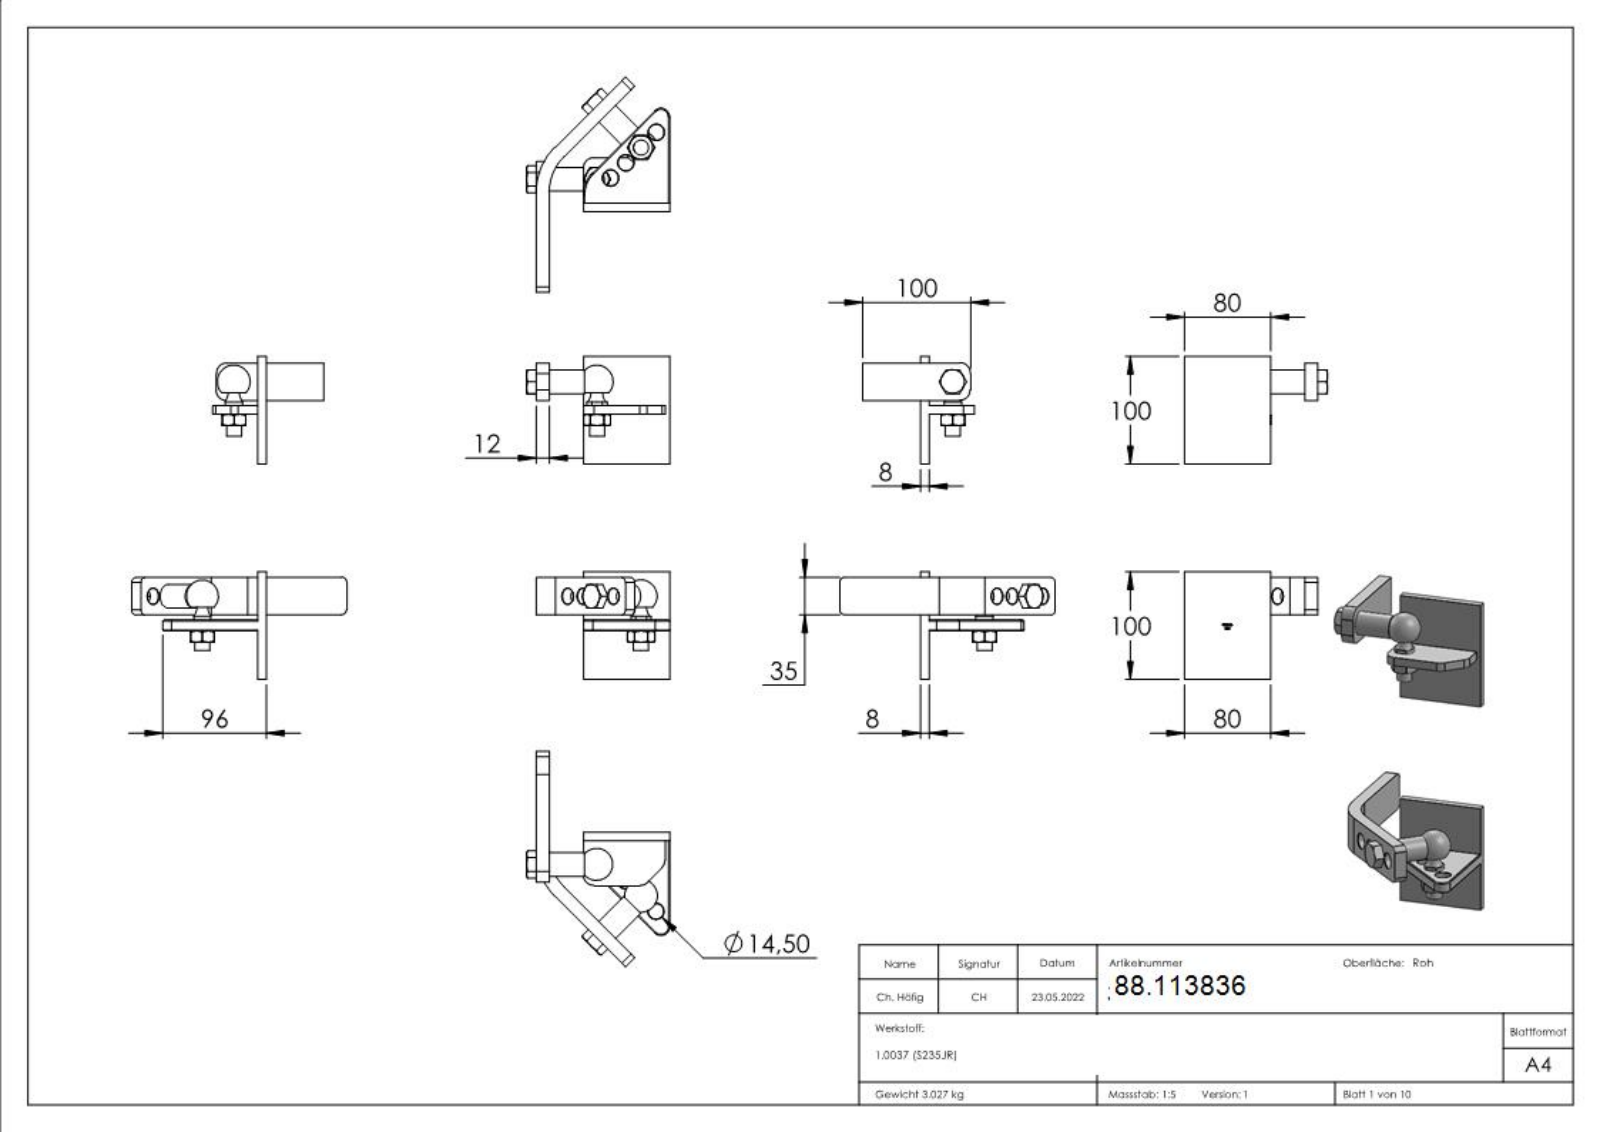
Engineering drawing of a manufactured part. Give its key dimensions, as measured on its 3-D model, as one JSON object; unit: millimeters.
{"part_name": "3836 Teil7_3836 Teil7; 3836 Teil3_3836 Teil3; 3836; 3836 Teil1_3836 Teil1 (+5 more)", "step_written_by": "SolidWorks 2018 (CONFIG_CONTROL_DESIGN)", "units": "millimeters", "bodies": {"solids": 12, "faces": 549, "planar": 180, "cylindrical": 59, "other": 310}, "overall_size": [300, 200, 132.87], "volume_mm3": 388104, "surface_area_mm2": 121724, "round_holes": [[14.5, 10], [12, 4], [19.5, 2]], "round_bosses_or_shafts": [[14, 4], [22.36, 2], [22, 2], [14.1, 2], [13, 2]], "partial_cylinders_radius": [[0.5, 12], [10, 5], [5, 4], [9.4, 2], [8, 1], [29.66, 1], [48, 1], [60, 1]], "face_to_face_distances": [8, 12, 199, 10, 39.66, 4.66, 35, 201, 191, 209], "hole_center_spacings": [20, 39.99, 59.99, 12.64, 30.8, 50.37, 70.19]}
